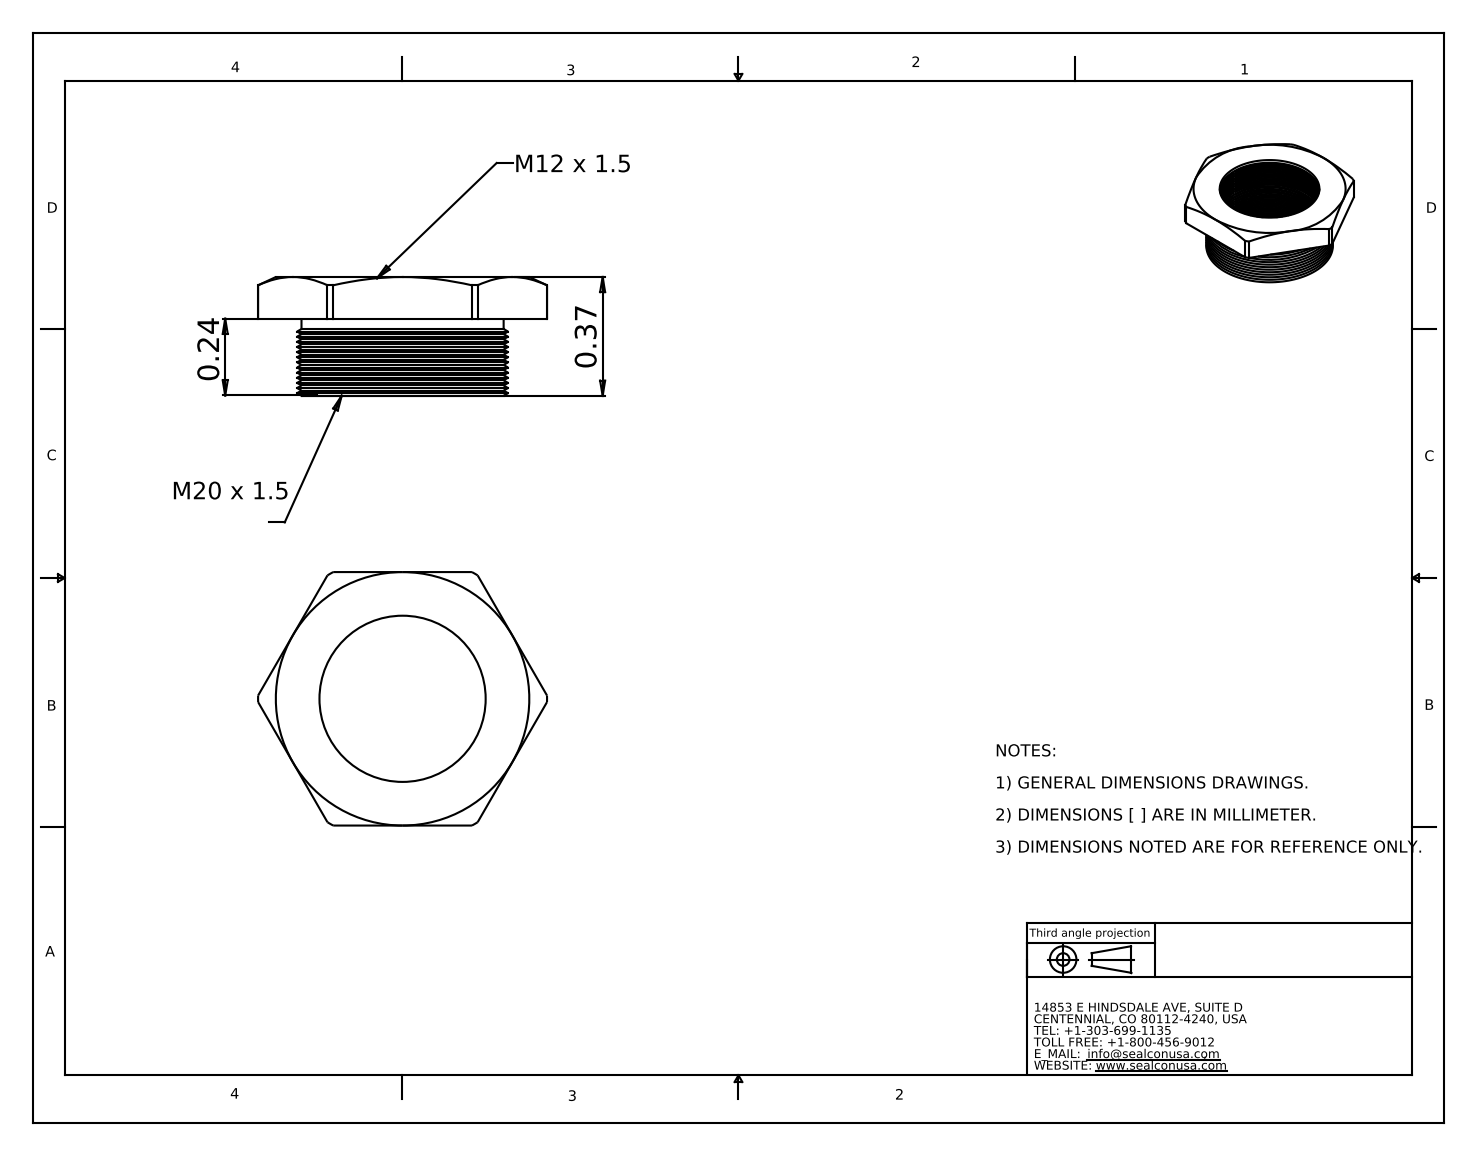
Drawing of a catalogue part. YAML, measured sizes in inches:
part_name: "RM-2012-SS"
step_written_by: "SolidWorks 2008 (CONFIG_CONTROL_DESIGN)"
units: inches
bodies: {solids: 1, faces: 241, planar: 9, cylindrical: 81, other: 151}
overall_size: [0.901, 0.79, 0.37]
volume: 0.068
surface_area: 3.098
round_holes:
  - {diameter: 0.518, count: 1}
round_bosses_or_shafts:
  - {diameter: 0.63, count: 1}
partial_cylinders:
  - {radius: 0.45, count: 1}
face_to_face_distances: [0.13, 0.79, 0.24, 0.37]
